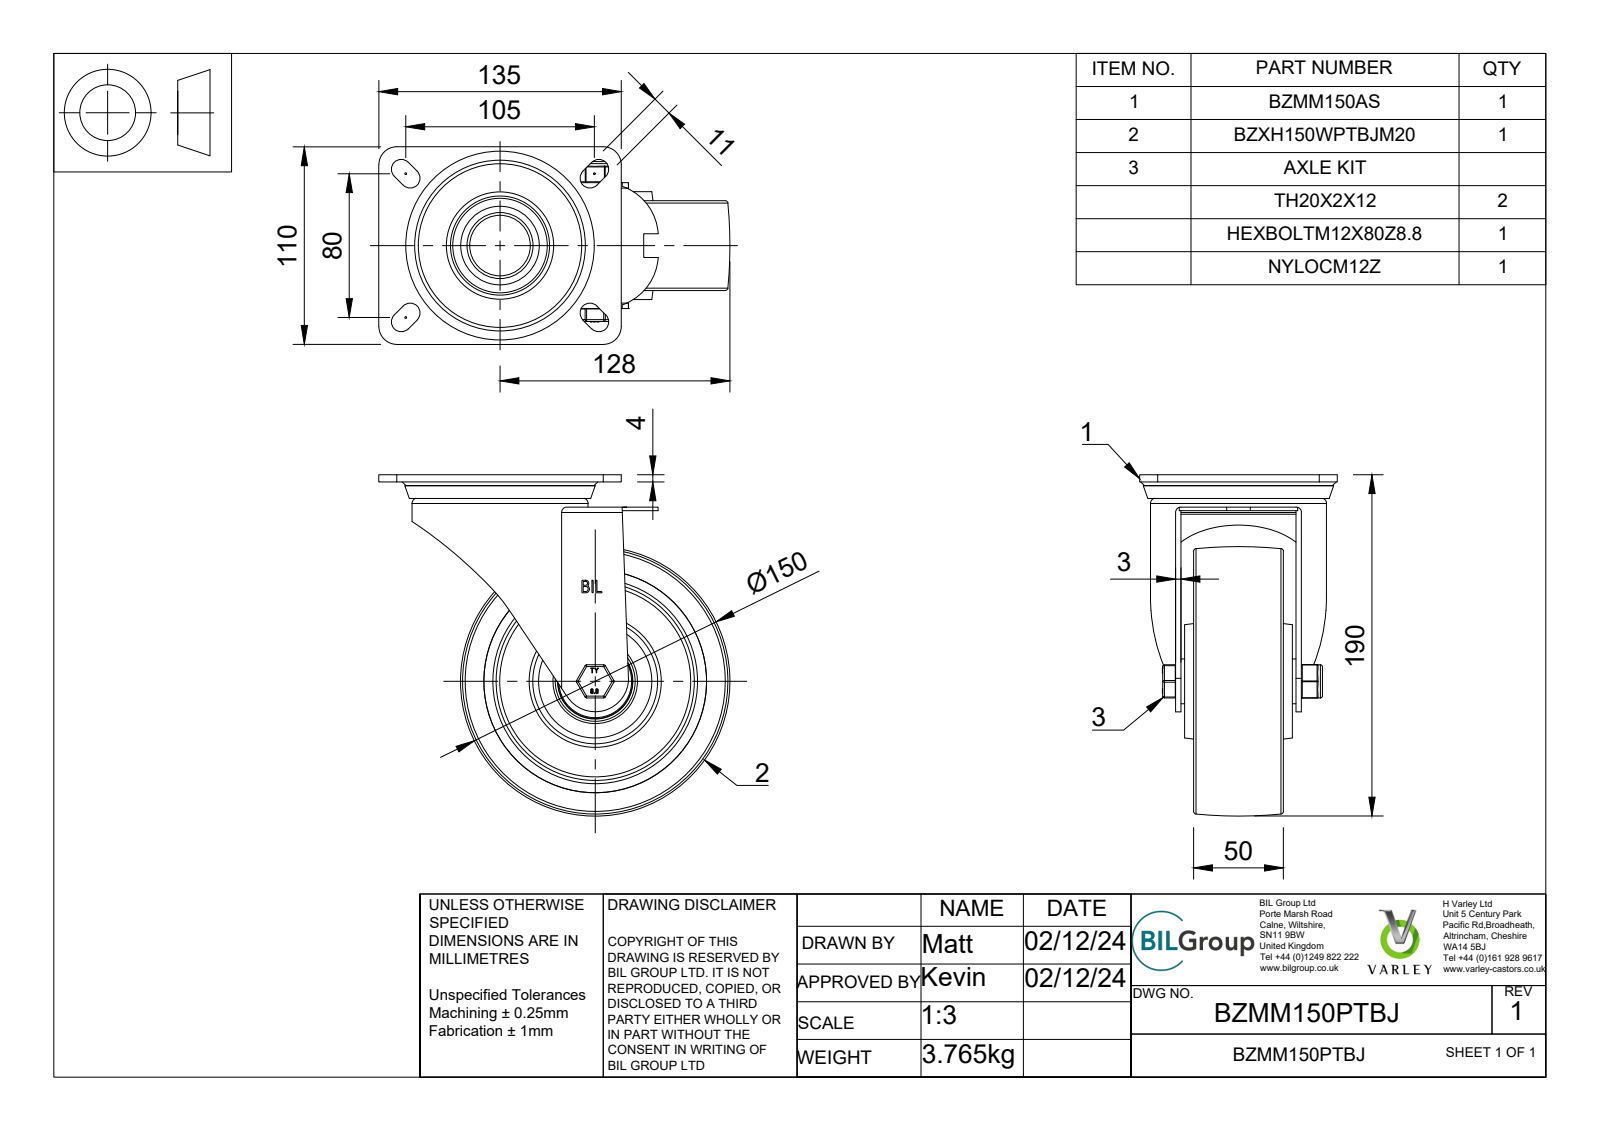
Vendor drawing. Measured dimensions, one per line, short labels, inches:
name: BZMM150PTBJ v3; BZMM150AS - 2 - 64 v2; ZINC PLATED, PRESSED STEEL TOP PLATE (1); ZINC PLATED, PRESSED STEEL TOP PLATE Geometry (1) (+8 more)
written by: Autodesk Translation Framework v13.20.0.188 (AP242_MANAGED_MODEL_BASED_3D_ENGINEERING_MIM_LF)
unit: in
bodies: 77 solids, 1353 faces (592 planar, 266 cylindrical, 495 other)
size: 7.697 × 7.48 × 4.331
volume: 46.14 in³; area: 436.3 in²
holes: 1× ⌀0.472, 1× ⌀0.48, 1× ⌀0.551, 1× ⌀0.787, 1× ⌀1.122, 1× ⌀1.329, 1× ⌀1.565, 1× ⌀1.634, 1× ⌀1.654, 1× ⌀1.732, 1× ⌀1.85, 1× ⌀3.622
bosses: 1× ⌀3.858, 1× ⌀3.071, 1× ⌀1.969, 1× ⌀1.594, 1× ⌀1.575, 1× ⌀1.142, 1× ⌀1.063, 1× ⌀0.984
rounds: 18× R0.02, 12× R0.039, 10× R0.157, 10× R0.236, 8× R0.217, 4× R0.394, 2× R0.059, 2× R0.118
face distances: 0.197, 0.354, 0.276, 0.118, 0.157, 0.079, 0.63, 2.362, 0.866, 1.102
